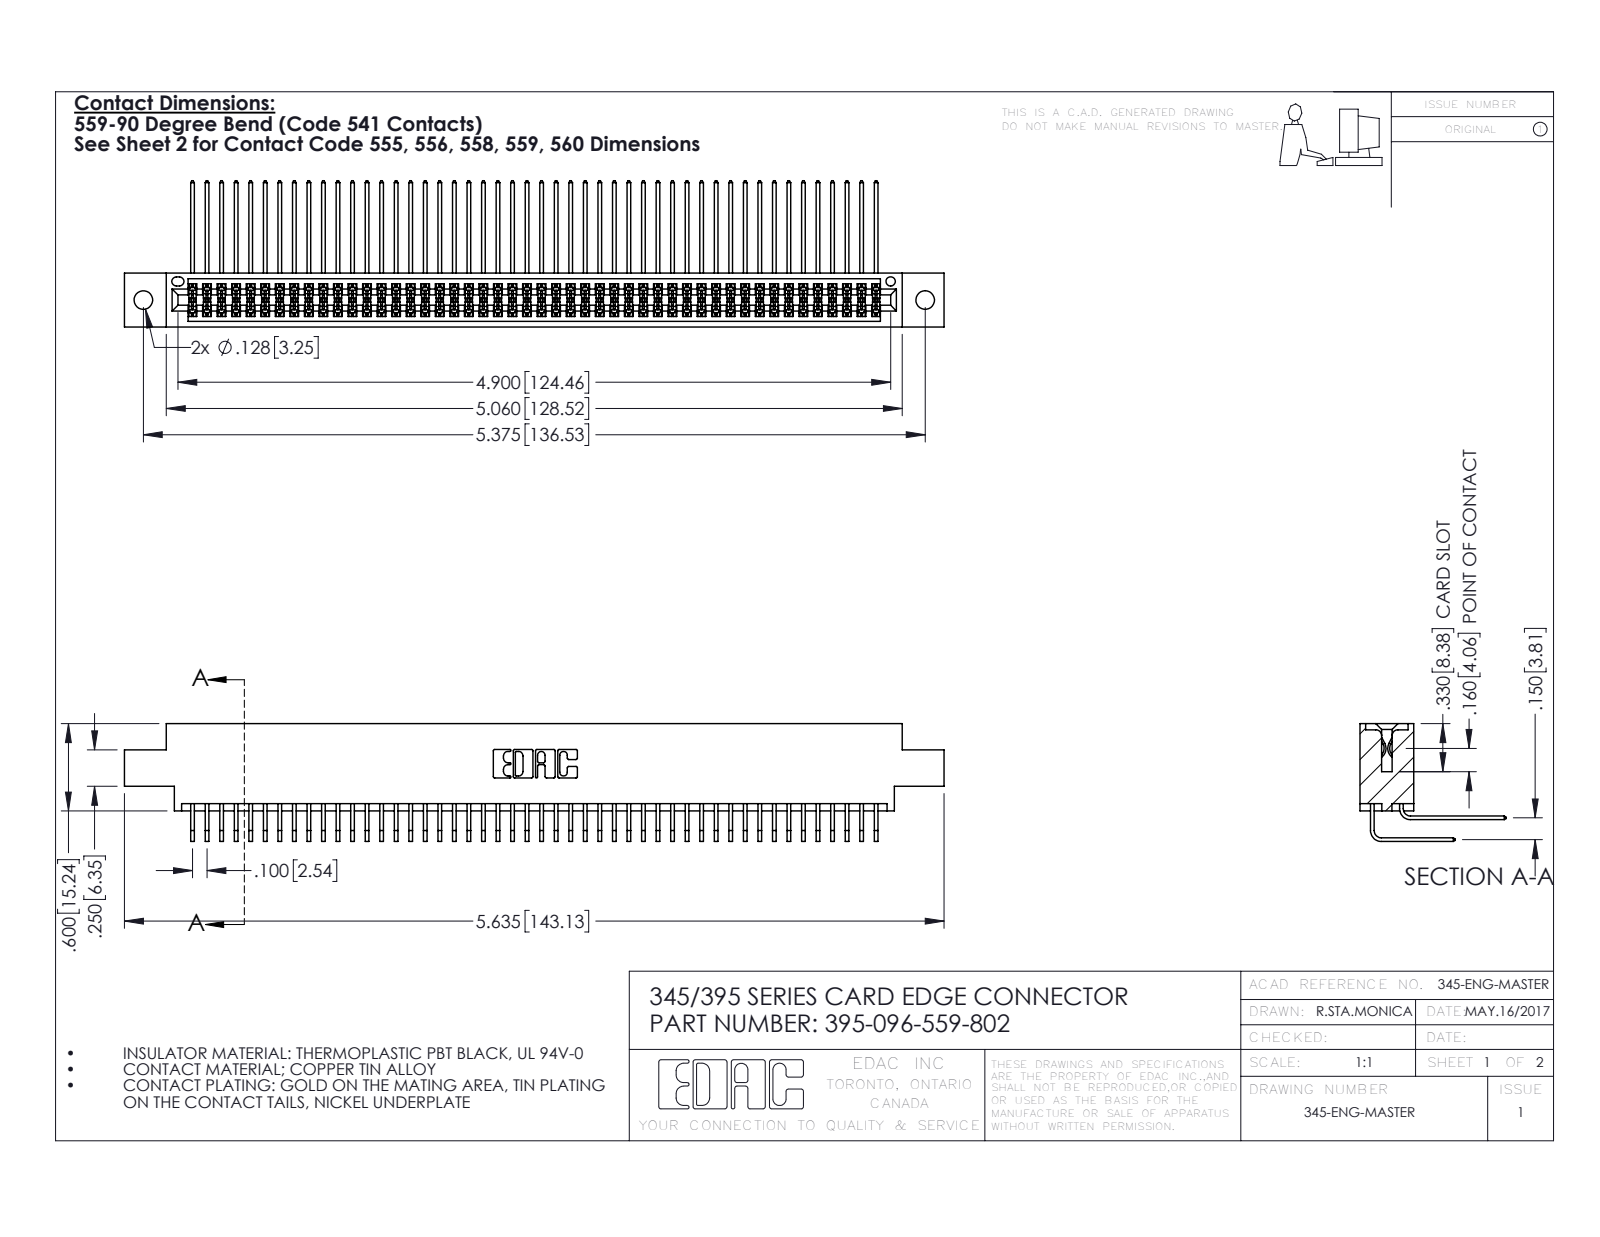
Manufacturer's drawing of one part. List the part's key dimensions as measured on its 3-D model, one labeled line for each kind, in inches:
Part name (STEP PRODUCT): 395-096-559-802; 345-292-001_558 559 Tail - 1; 345 Part_0.170 Offset - 0.128 Dia; 345-292-001_559 Tail - 2
STEP written by: SolidWorks 2016 (CONFIG_CONTROL_DESIGN)
Units: inches
Bodies: 97 solids, 5122 faces (3444 planar, 1678 cylindrical, 0 other)
Overall size (bounding box): 5.635 × 1.005 × 0.809
Volume: 0.876 in³ · Surface area: 36.92 in²
Round holes (diameter × count): ⌀0.128 ×2, ⌀0.064 ×1
Partial cylindrical surfaces — rounded edges, fillets, slot ends (radius × count): R0.006 ×144, R0.01 ×22, R0.007 ×6, R0.031 ×6, R0.026 ×3, R0.014 ×2, R0.019 ×2, R0.022 ×2
Main face-to-face distances: 0.072, 0.298, 0.37, 0.2, 0.098, 0.272, 0.025, 0.225, 0.175, 0.15
Hole centre spacings: 0.27, 5.139, 5.375
